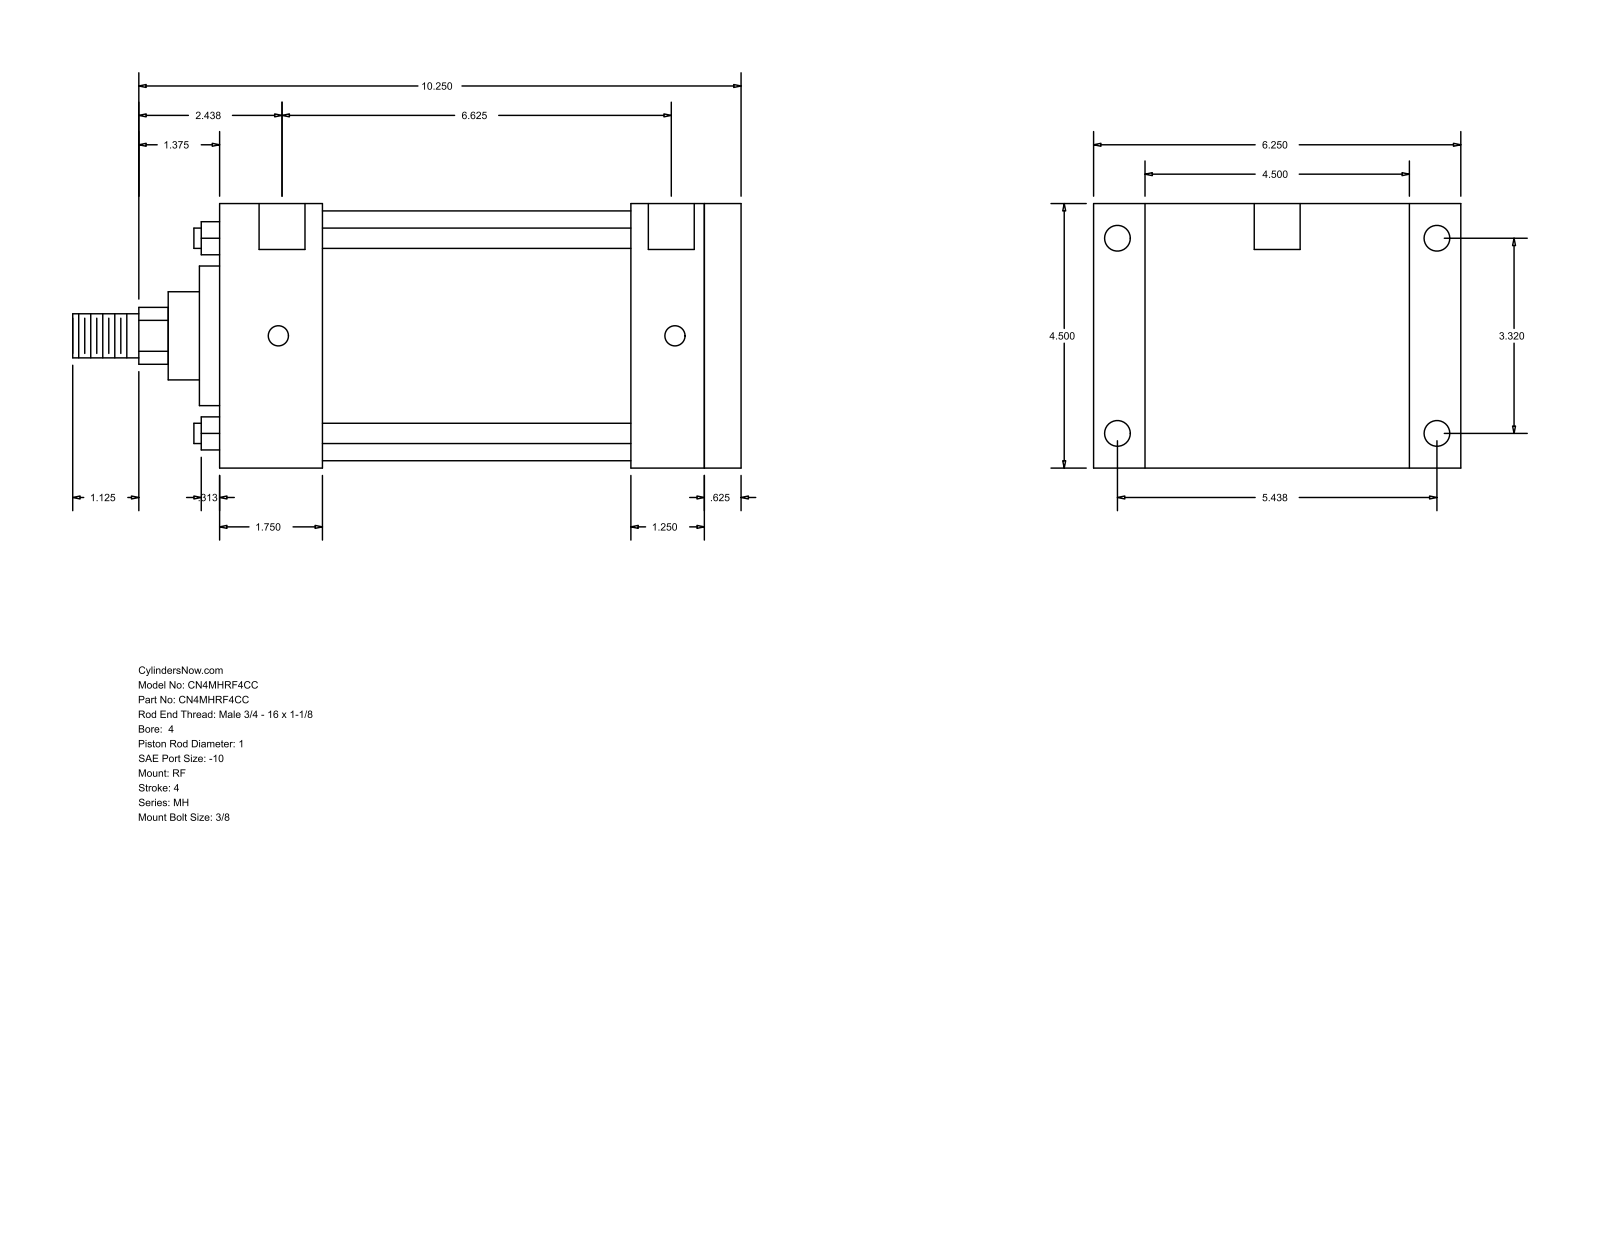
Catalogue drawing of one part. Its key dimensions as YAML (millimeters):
part_name: "MH_RF__0400_1"
step_written_by: "GSSL Pune (CONFIG_CONTROL_DESIGN)"
units: millimeters
bodies: {solids: 0, faces: 94, planar: 65, cylindrical: 29, other: 0}
overall_size: [288.93, 158.75, 114.3]
round_holes:
  - {diameter: 8.73, count: 4}
  - {diameter: 11.13, count: 4}
  - {diameter: 19.84, count: 2}
round_bosses_or_shafts:
  - {diameter: 8.76, count: 4}
  - {diameter: 107.95, count: 1}
  - {diameter: 60.33, count: 1}
  - {diameter: 38.1, count: 1}
  - {diameter: 25.4, count: 1}
  - {diameter: 19.05, count: 1}
partial_cylinders:
  - {radius: 12.29, count: 1}
face_to_face_distances: [114.3, 225.43, 209.55, 15.88, 47.63, 44.46, 165.09, 180.97, 177.8, 133.34]
hole_center_spacings: [84.32, 138.12, 161.82, 171.45, 1.58, 1.59, 168.28, 169.86]
